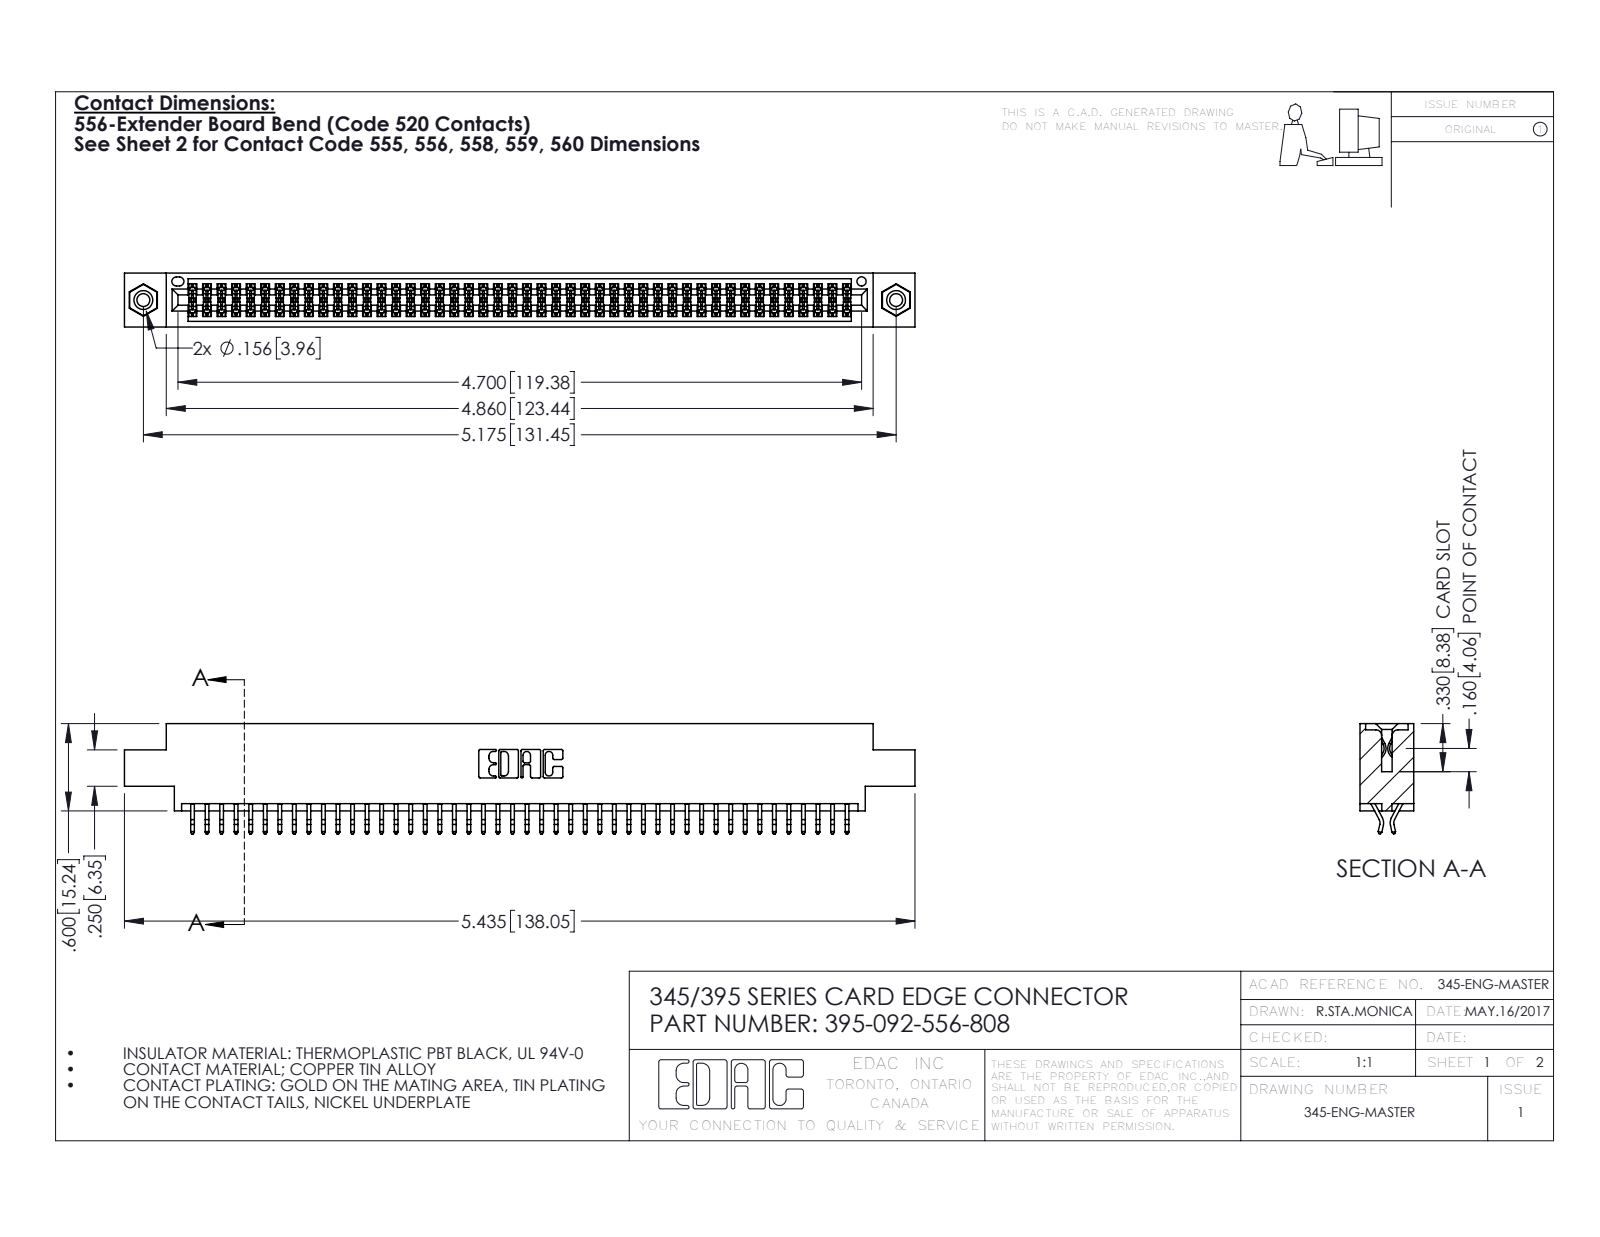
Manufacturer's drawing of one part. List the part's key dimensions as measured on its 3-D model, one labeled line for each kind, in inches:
Part name (STEP PRODUCT): 345-250-001_345-250-003-102; 345-292-001_556 Tail; 395-092-556-808; 345 Part_0.170 Offset - 0.156 Dia-TI
STEP written by: SolidWorks 2016 (CONFIG_CONTROL_DESIGN)
Units: inches
Bodies: 95 solids, 5342 faces (3520 planar, 1806 cylindrical, 16 other)
Overall size (bounding box): 5.435 × 0.757 × 0.37
Volume: 0.813 in³ · Surface area: 30.77 in²
Round holes (diameter × count): ⌀0.089 ×2, ⌀0.125 ×2, ⌀0.156 ×2, ⌀0.064 ×1
Round bosses / shafts (diameter × count): ⌀0.155 ×2
Partial cylindrical surfaces — rounded edges, fillets, slot ends (radius × count): R0.006 ×138, R0.01 ×22, R0.007 ×6, R0.031 ×6, R0.026 ×3, R0.01 ×2, R0.014 ×2, R0.019 ×2
Main face-to-face distances: 0.072, 0.298, 0.37, 0.2, 0.025, 0.098, 0.272, 0.225, 0.175, 0.149
Hole centre spacings: 0.27, 4.939, 5.175
